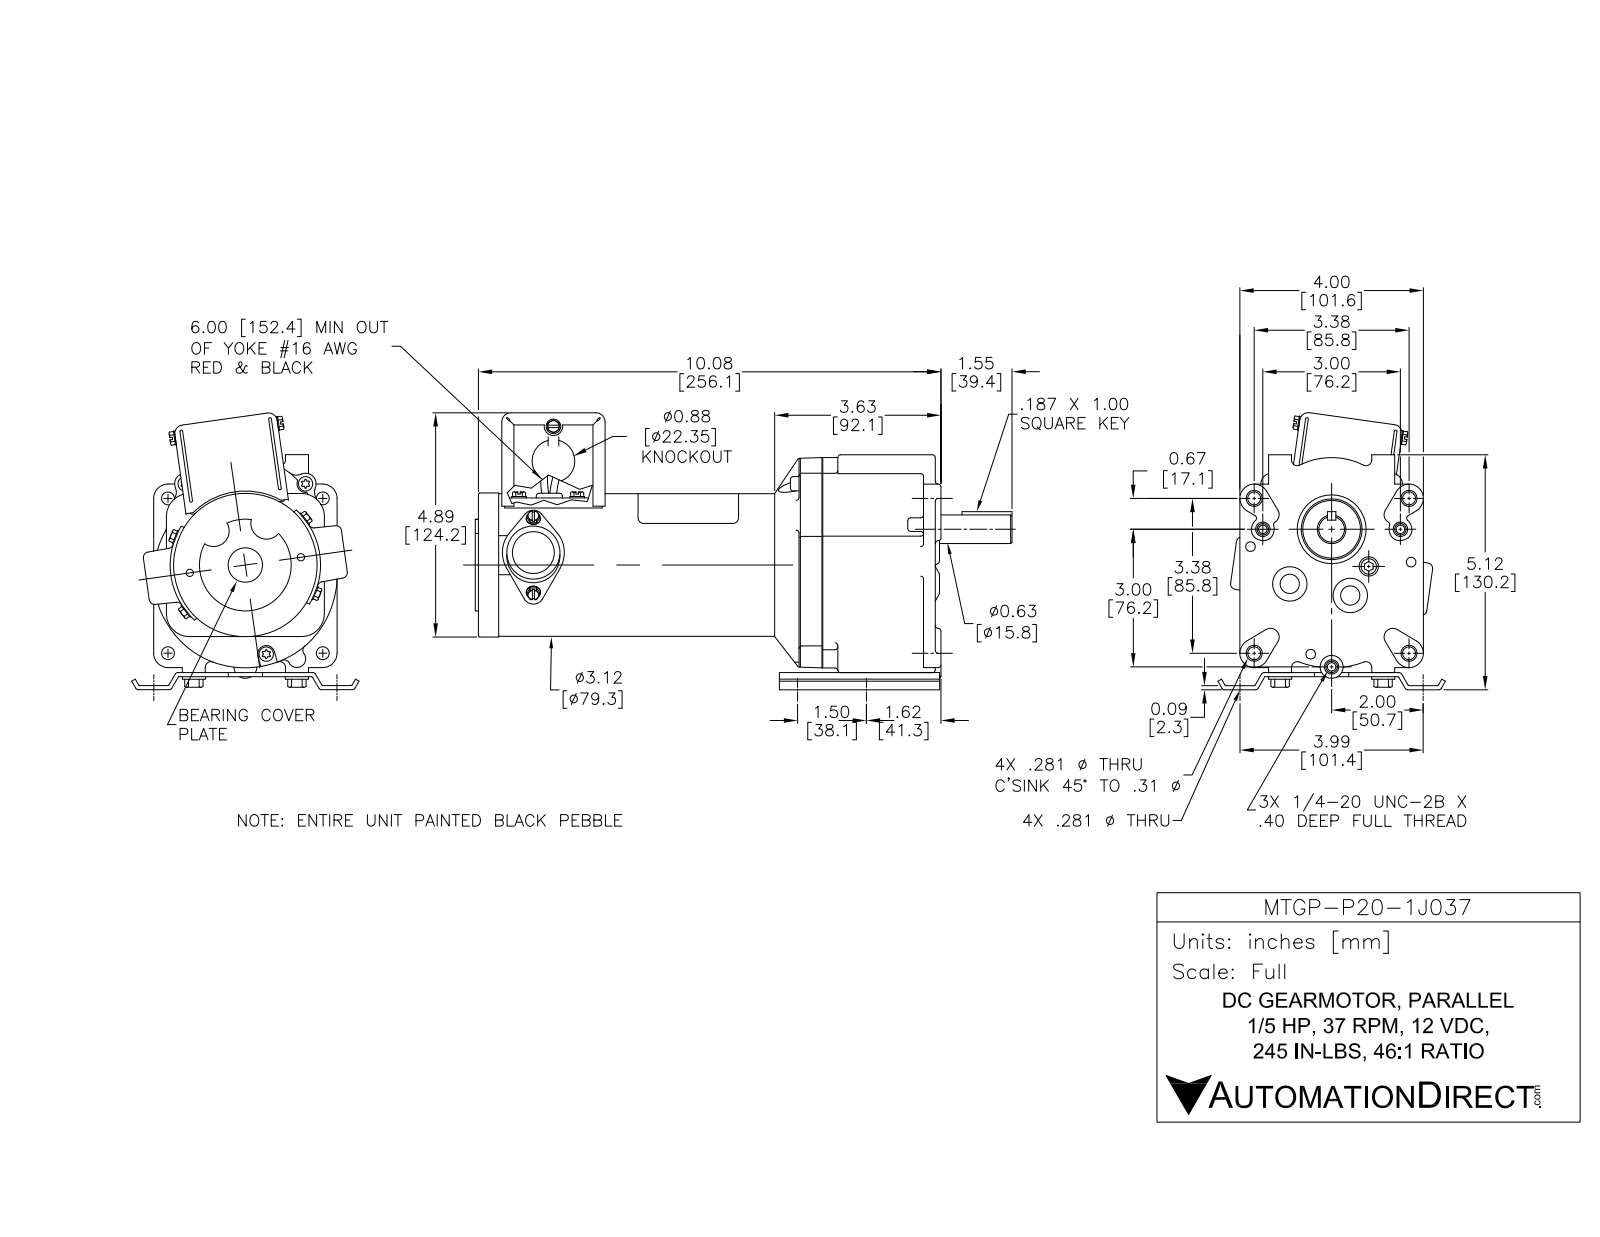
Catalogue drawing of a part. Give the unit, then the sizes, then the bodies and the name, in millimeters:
Units: millimetres
Overall size (bounding box): 297.1 × 157.7 × 125.5
Round holes (diameter × count): ⌀7.6 ×11, ⌀12.7 ×5, ⌀6.4 ×4, ⌀8.8 ×4, ⌀5.3 ×3, ⌀3.2 ×2, ⌀5 ×2, ⌀5.3 ×2, ⌀8.8 ×2, ⌀9.5 ×1, ⌀11.7 ×1, ⌀15.9 ×1
Round bosses / shafts (diameter × count): ⌀8 ×5, ⌀7.6 ×4, ⌀5.3 ×3, ⌀11.7 ×2, ⌀2.5 ×2, ⌀80.2 ×1, ⌀33.7 ×1, ⌀15.9 ×1
Partial cylindrical surfaces — rounded edges, fillets, slot ends (radius × count): R0.5 ×28, R2.5 ×23, R0.6 ×8, R6.4 ×7, R4 ×4, R4.8 ×4, R4.9 ×4, R5.9 ×4
Main face-to-face distances: 34.9, 88.8, 53.8, 2.3, 0.8, 6.4, 1.6, 1.3, 36.2, 90
Hole centre spacings: 41.1, 31.2, 38.1, 38.2, 40.7, 75.5, 85.7, 175.5
Volume: 1 067 000 mm³ · Surface area: 303 600 mm²
Bodies: 53 solids, 984 faces (567 planar, 365 cylindrical, 52 other)
Part name (STEP PRODUCT): MTGP-P20-1J037
STEP written by: SolidWorks 2014 (AUTOMOTIVE_DESIGN)
